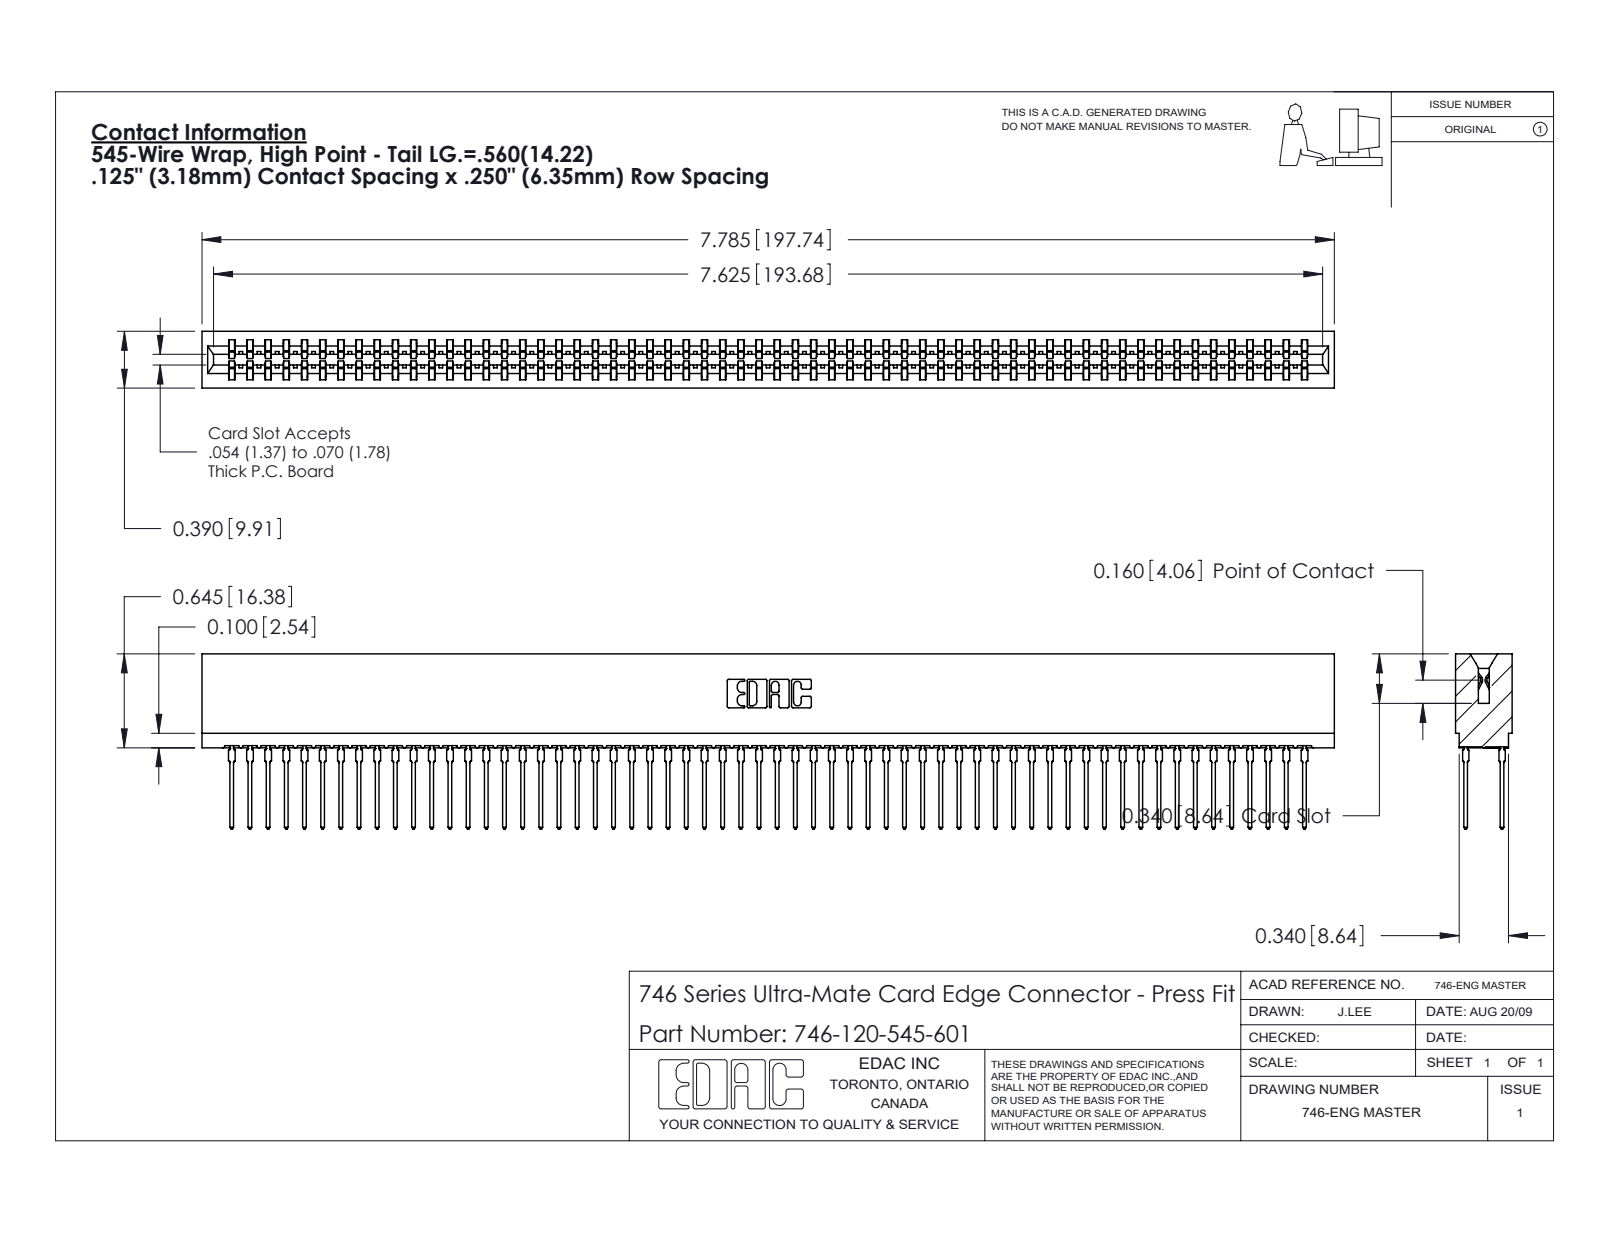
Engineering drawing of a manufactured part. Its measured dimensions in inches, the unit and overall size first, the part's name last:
Units: inches
Overall size (bounding box): 7.785 × 1.204 × 0.39
Partial cylindrical surfaces — rounded edges, fillets, slot ends (radius × count): R0.021 ×240, R0.015 ×61, R0.01 ×22, R0.005 ×8, R0.011 ×8, R0.007 ×6, R0.031 ×6, R0.026 ×3
Main face-to-face distances: 0.057, 0.333, 0.39, 0.025, 0.25, 0.307, 0.275, 0.083, 0.015, 0.059
Volume: 1.406 in³ · Surface area: 55.94 in²
Bodies: 121 solids, 10837 faces (5575 planar, 2142 cylindrical, 3120 other)
Part name (STEP PRODUCT): 746 Part_.340 Slot Depth - 01; 746-120-545-601; 746-292-001_545
STEP written by: SolidWorks 2020 (CONFIG_CONTROL_DESIGN)
